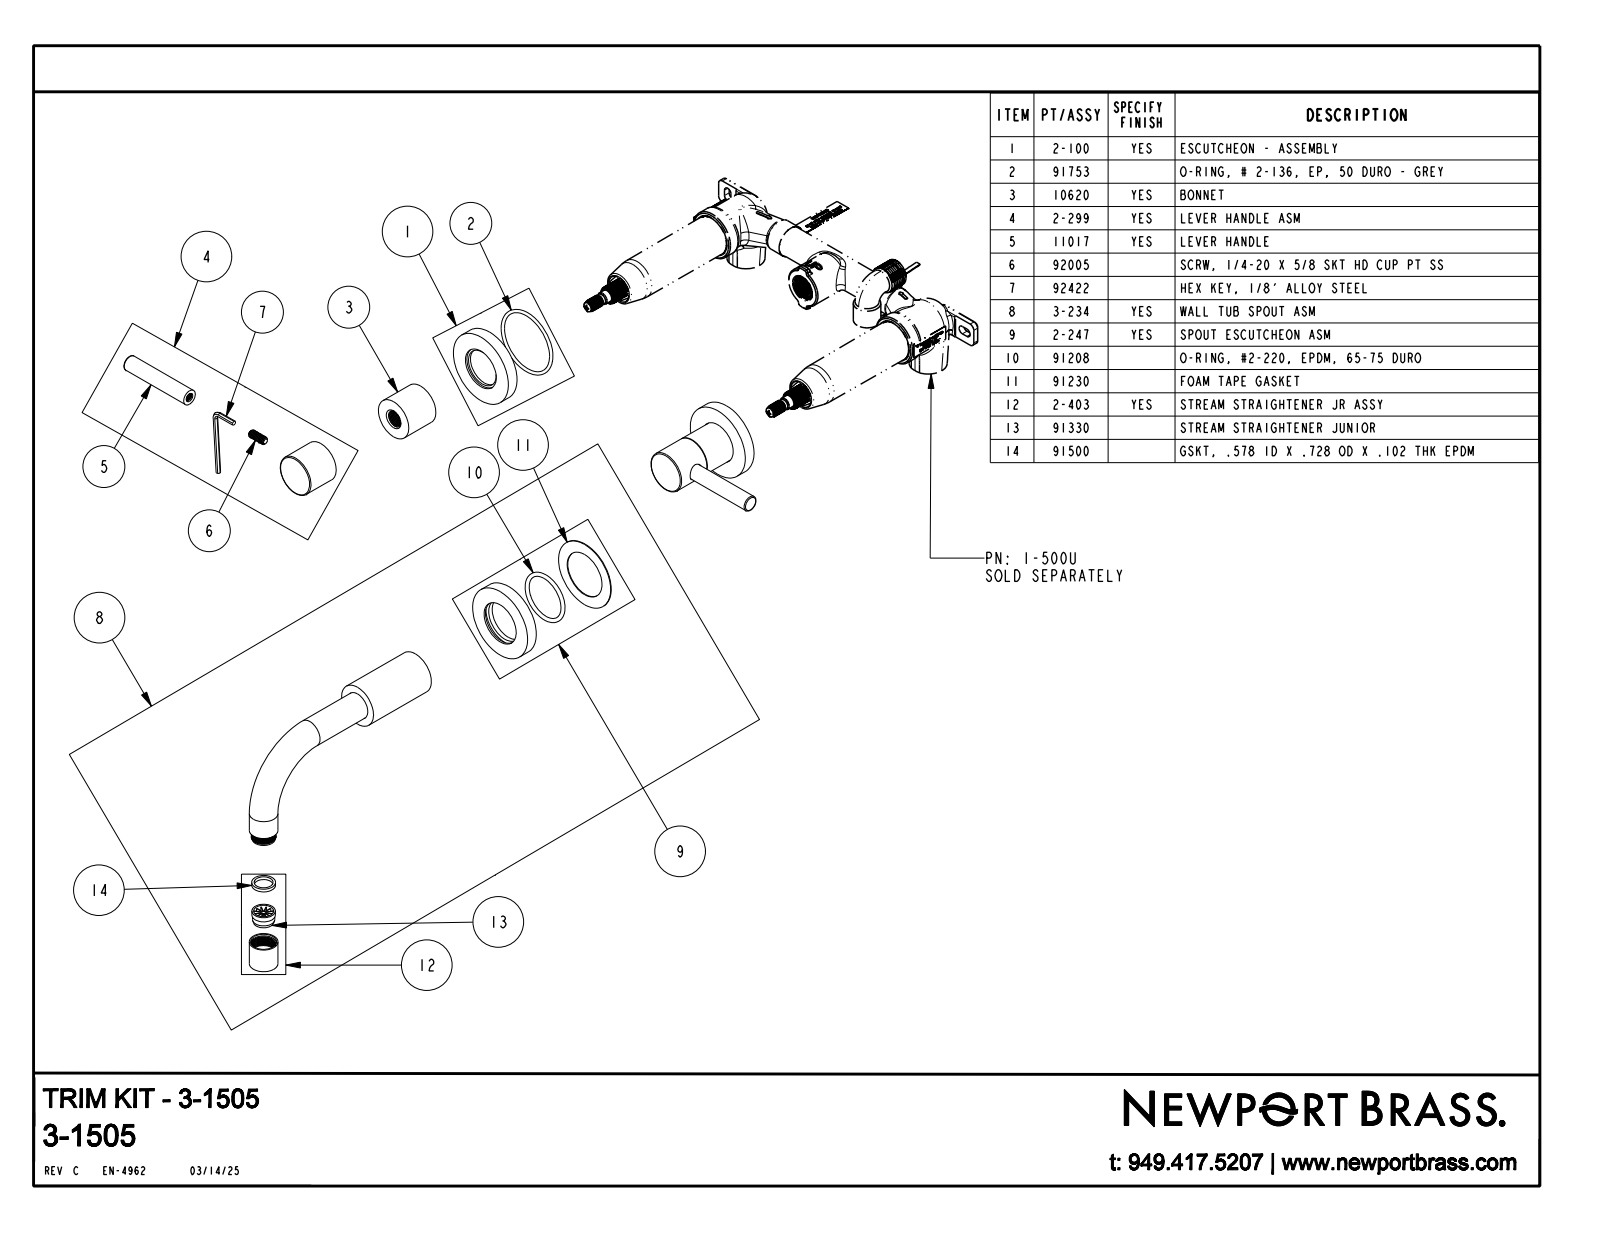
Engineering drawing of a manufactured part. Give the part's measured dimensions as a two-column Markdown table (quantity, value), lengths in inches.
| quantity | value |
| --- | --- |
| part name | 3-1505_SW0001 |
| STEP written by | CREO PARAMETRIC BY PTC INC, 2018400 (AUTOMOTIVE_DESIGN) |
| units | inches |
| bodies | 3 solids, 60 faces (18 planar, 32 cylindrical, 10 other) |
| overall size | 13.888 × 10.627 × 5.998 |
| volume | 17.6 in³ |
| surface area | 89.89 in² |
| round holes (diameter × count) | 0.52 × 1 |
| round bosses / shafts (diameter × count) | 2.375 × 3, 0.5 × 3, 1.313 × 2, 1.312 × 2, 0.875 × 2, 1.375 × 1 |
| main face-to-face distances | 0.375, 2.623, 2.248, 1.483, 1.108, 1.14, 1.503, 1.128, 0.02, 1.12 |
